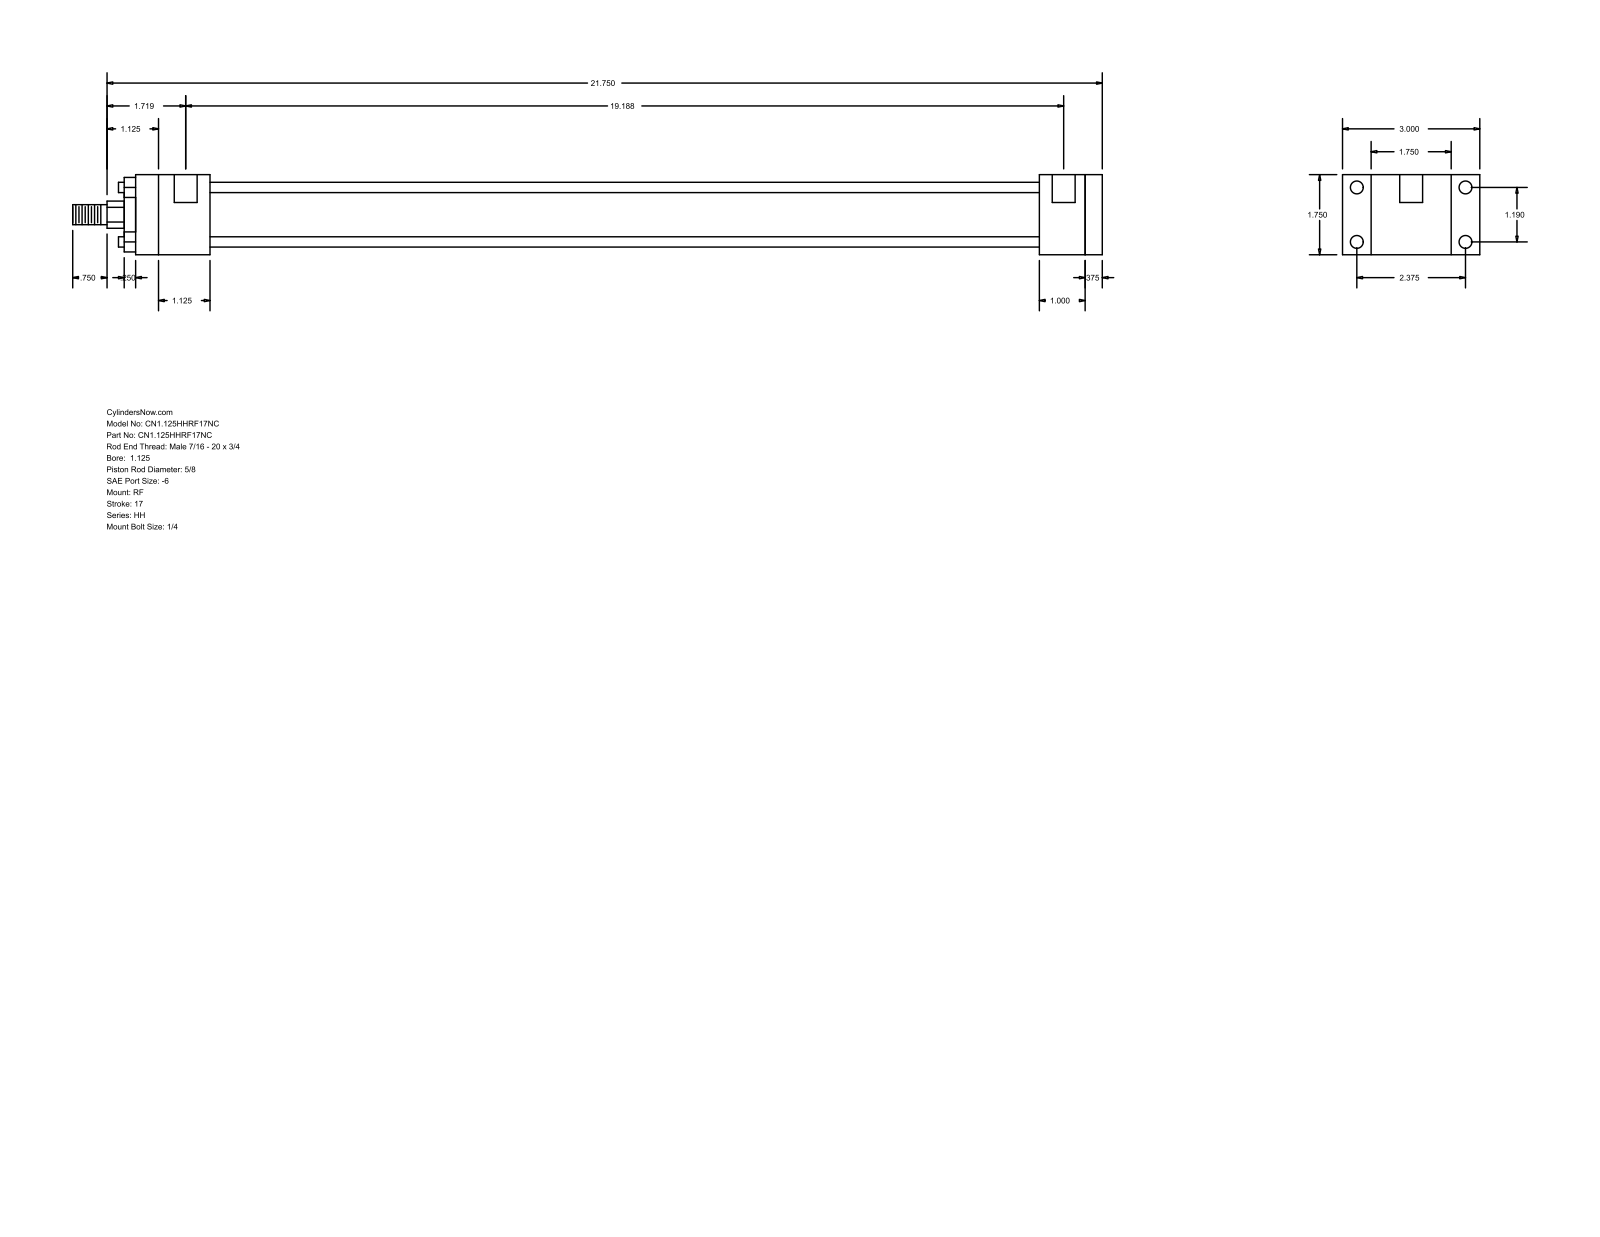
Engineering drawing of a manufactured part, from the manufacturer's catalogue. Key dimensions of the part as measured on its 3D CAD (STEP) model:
Part name (STEP PRODUCT): HH_RF__0112_0.625
STEP written by: GSSL Pune (CONFIG_CONTROL_DESIGN)
Units: millimetres
Bodies: 0 solids, 92 faces (64 planar, 28 cylindrical, 0 other)
Overall size (bounding box): 571.5 × 76.2 × 44.45
Round holes (diameter × count): ⌀5.56 ×4, ⌀7.14 ×4, ⌀12.7 ×2
Round bosses / shafts (diameter × count): ⌀5.71 ×4, ⌀34.92 ×1, ⌀28.57 ×1, ⌀15.88 ×1, ⌀11.11 ×1
Partial cylindrical surfaces — rounded edges, fillets, slot ends (radius × count): R7.54 ×1
Main face-to-face distances: 44.46, 9.53, 536.57, 25.4, 34.93, 15.87, 485.77, 495.3, 460.37, 41.27
Hole centre spacings: 30.22, 60.32, 67.47, 484.19, 3.17, 487.36
